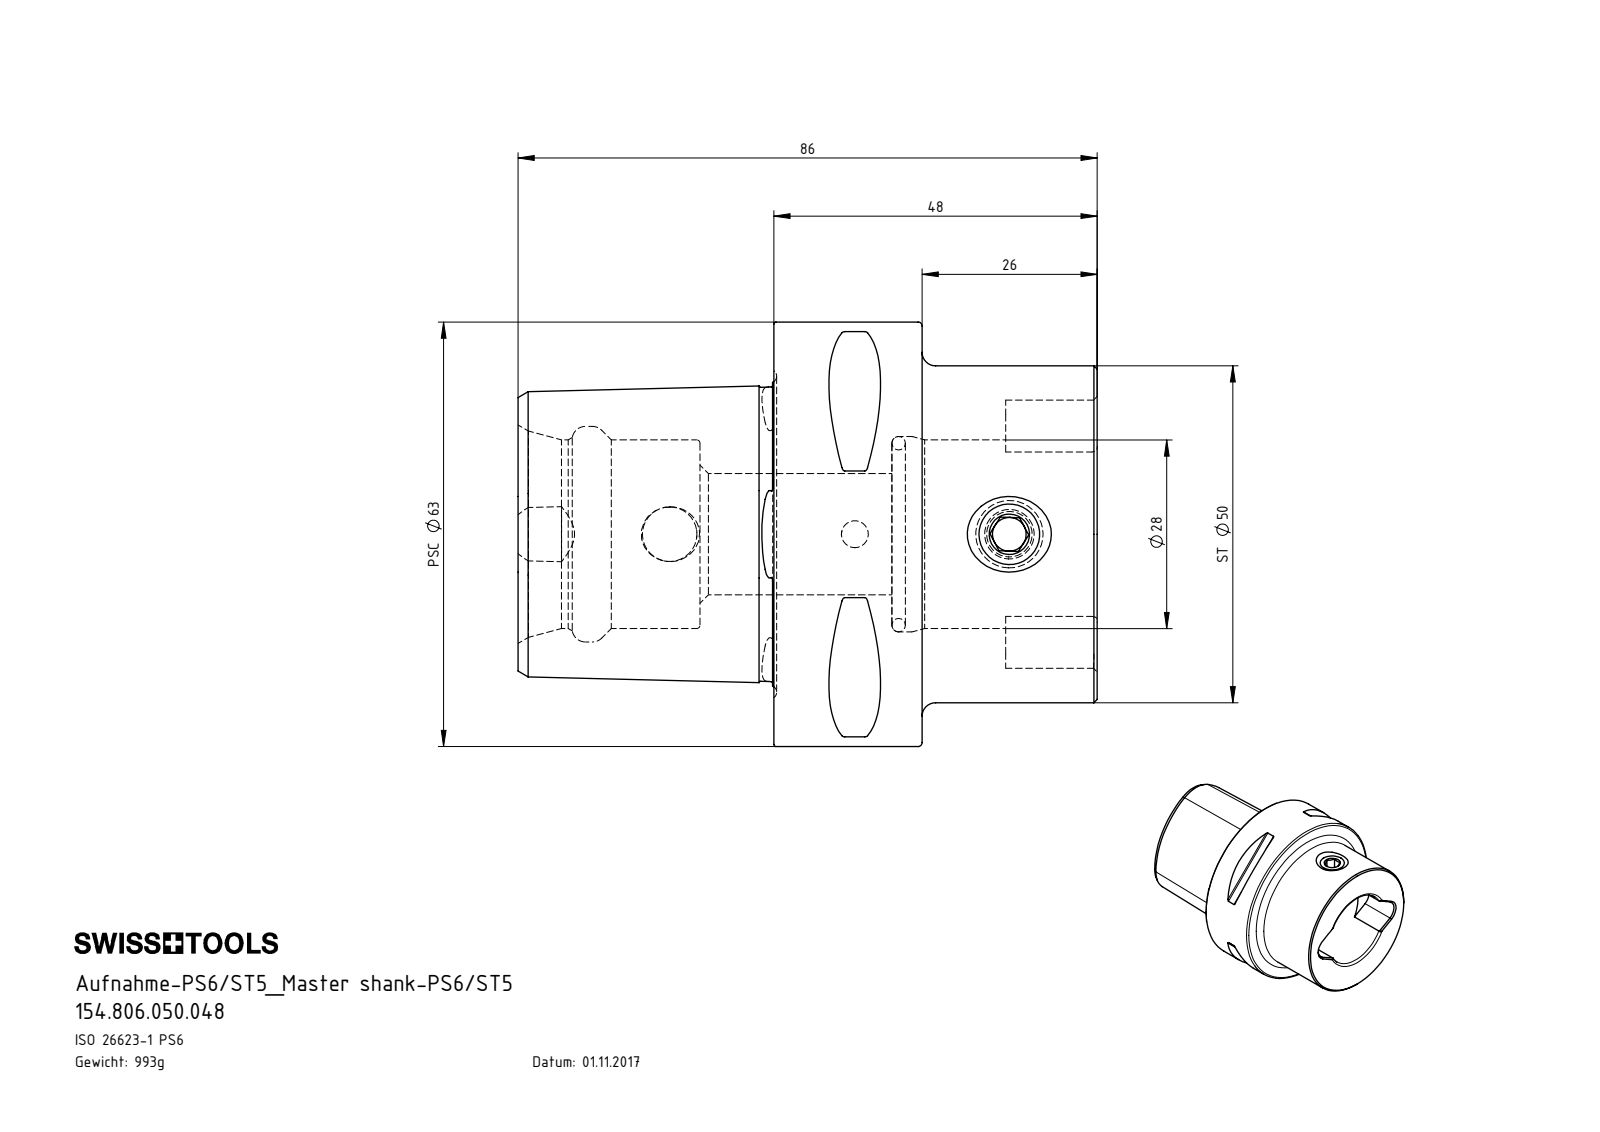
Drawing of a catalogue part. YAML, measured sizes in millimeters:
part_name: "ST5-ER1.001.012_A; PS6-ST5.K01.048_B; DIN 3771 - 25x2; PS6.ST5.K01.048"
step_written_by: "SolidWorks 2017 (AUTOMOTIVE_DESIGN)"
units: millimeters
bodies: {solids: 3, faces: 131, planar: 43, cylindrical: 25, other: 63}
overall_size: [86, 63, 63]
volume: 126779
surface_area: 27643
round_holes:
  - {diameter: 4, count: 1}
  - {diameter: 5, count: 1}
  - {diameter: 8.1, count: 1}
  - {diameter: 9, count: 1}
  - {diameter: 18, count: 1}
  - {diameter: 28, count: 1}
  - {diameter: 29, count: 1}
  - {diameter: 32, count: 1}
round_bosses_or_shafts:
  - {diameter: 63, count: 1}
  - {diameter: 50, count: 1}
  - {diameter: 10, count: 1}
partial_cylinders:
  - {radius: 0.5, count: 8}
  - {radius: 4.2, count: 2}
  - {radius: 6, count: 1}
face_to_face_distances: [48, 22, 26, 38, 60, 86, 55.5, 17.5, 4.5, 30.5]
hole_center_spacings: [22.95, 27.5, 50.45]
